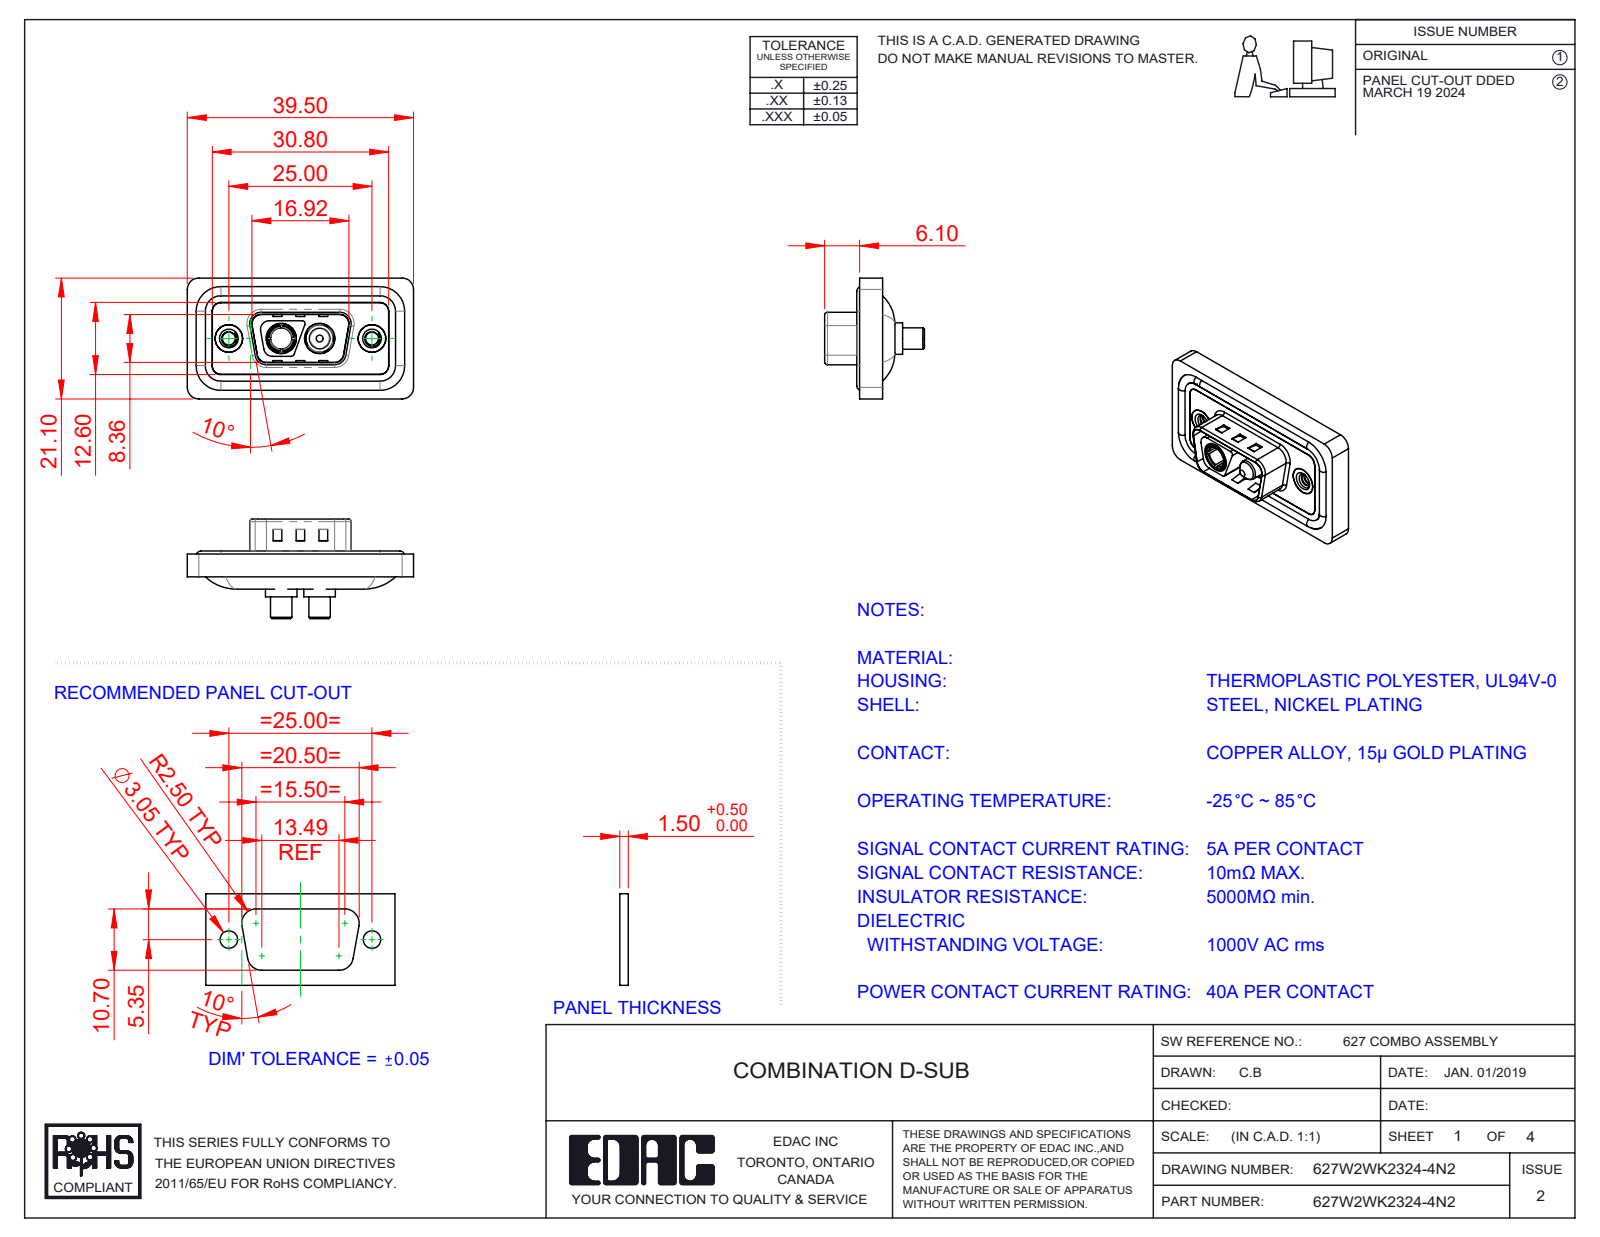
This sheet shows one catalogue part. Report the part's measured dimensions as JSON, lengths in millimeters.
{"part_name": "627Combo Shell Front_09 Contacts; 627Combo Threaded Rivet_2; 627Combo Housing_2WK2; Power Pin_40A S (+4 more)", "step_written_by": "SolidWorks 2023 (CONFIG_CONTROL_DESIGN)", "units": "millimeters", "bodies": {"solids": 11, "faces": 534, "planar": 189, "cylindrical": 227, "other": 118}, "overall_size": [39.5, 21.1, 17.4], "volume_mm3": 4591, "surface_area_mm2": 7364, "round_holes": [[2.26, 2], [4, 2], [4.8, 2], [4.85, 2], [5, 2], [5.3, 2], [3.7, 1]], "round_bosses_or_shafts": [[1.6, 4], [5.5, 2], [5.2, 2], [4.9, 2], [4.75, 2], [3.75, 2], [4.96, 1], [3.6, 1]], "partial_cylinders_radius": [[1.5, 24], [2, 18], [0.5, 10], [1.6, 8], [0.25, 4], [0.6, 4], [0.65, 4], [0.9, 4]], "face_to_face_distances": [0.4, 1.1, 2.9, 0.5, 3.1, 1.6, 1.5, 2.5, 4, 1.8], "hole_center_spacings": [9.14, 15.86, 6.72, 25]}
